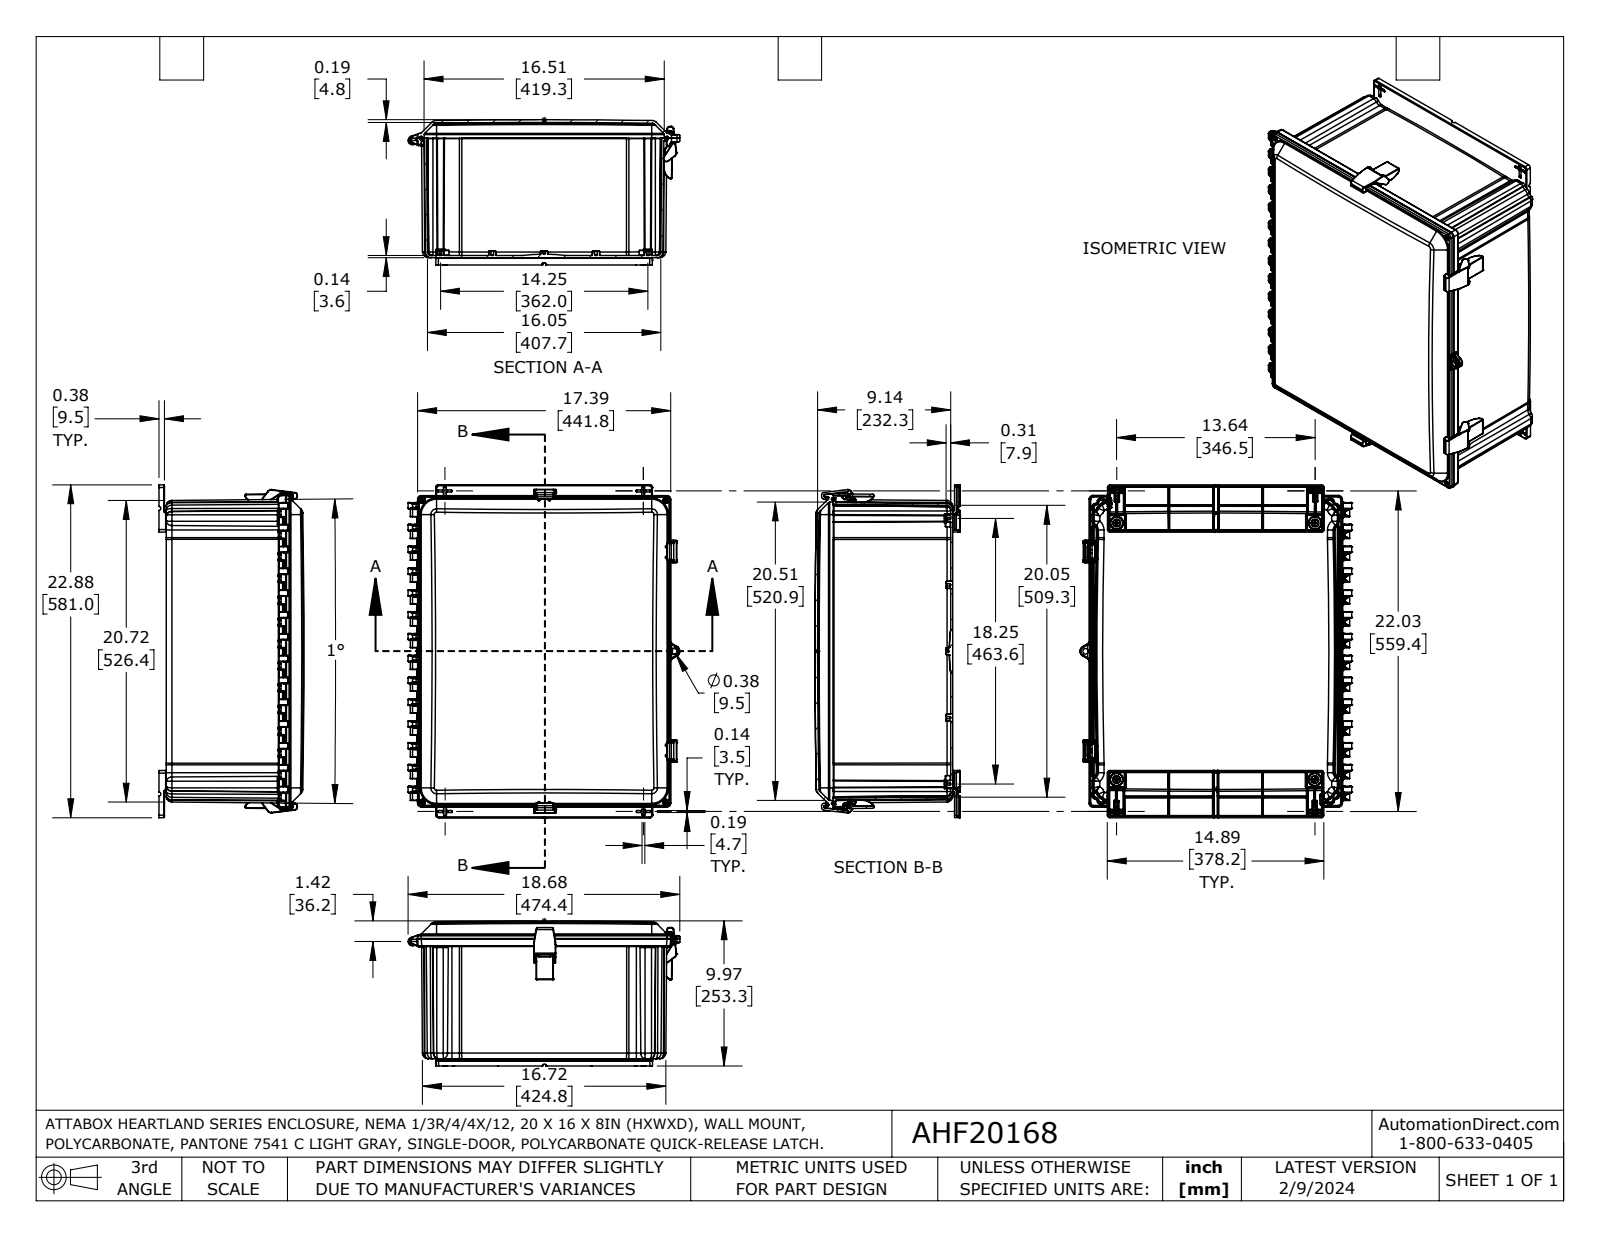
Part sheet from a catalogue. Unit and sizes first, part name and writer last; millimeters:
Units: millimetres
Overall size (bounding box): 581 × 474.4 × 253.3
Round holes (diameter × count): ⌀4.7 ×21, ⌀5 ×4, ⌀6.4 ×4, ⌀7.1 ×4, ⌀9.9 ×4, ⌀6.9 ×2, ⌀9.5 ×2, ⌀8.3 ×1, ⌀11.4 ×1
Round bosses / shafts (diameter × count): ⌀12.4 ×21, ⌀5.1 ×6, ⌀15.9 ×4, ⌀6.4 ×4, ⌀8 ×1
Partial cylindrical surfaces — rounded edges, fillets, slot ends (radius × count): R0.9 ×339, R1.7 ×49, R0.3 ×46, R0.5 ×21, R2.4 ×10, R0.6 ×9, R1.3 ×8, R6.2 ×8
Main face-to-face distances: 1.8, 3.6, 408.2, 509.8, 406.4, 208.4, 12.7, 410, 508, 511.6
Hole centre spacings: 147, 115.9, 90.5, 214.9, 248.8, 231.8, 181, 294.1
Volume: 4 039 000 mm³ · Surface area: 2 029 000 mm²
Bodies: 10 solids, 2516 faces (840 planar, 812 cylindrical, 864 other)
Part name (STEP PRODUCT): AHF20168C
STEP written by: SolidWorks 2023 (AUTOMOTIVE_DESIGN)
